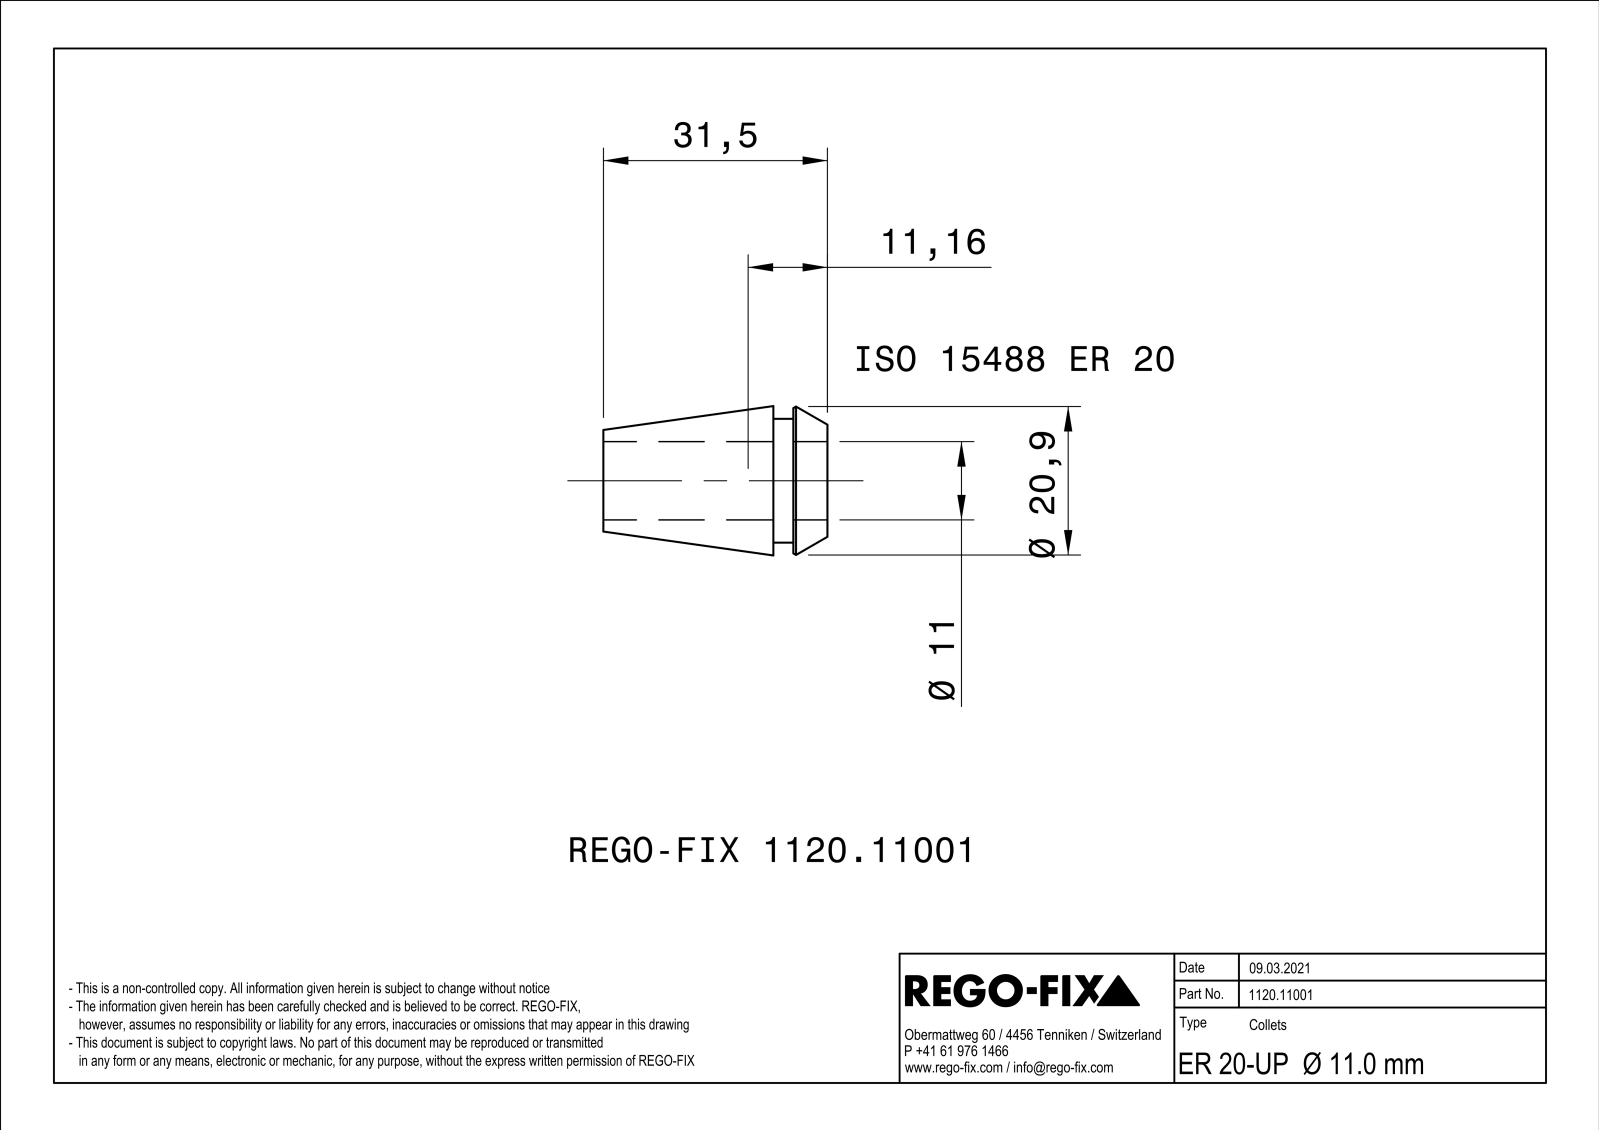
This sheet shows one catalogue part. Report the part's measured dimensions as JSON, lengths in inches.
{"part_name": "NOCUT", "step_written_by": "SIEMENS PLM Software Solid Edge ST10 (AUTOMOTIVE_DESIGN)", "units": "inches", "bodies": {"solids": 1, "faces": 177, "planar": 88, "cylindrical": 9, "other": 80}, "overall_size": [1.24, 0.826, 0.826], "volume_in3": 0.243, "surface_area_in2": 8.838, "round_holes": [[0.433, 1]], "round_bosses_or_shafts": [[0.685, 1]], "face_to_face_distances": [0.024, 0.299, 0.189, 0.11, 1.24, 1.051, 0.941, 0.217, 0.028, 0.083]}
